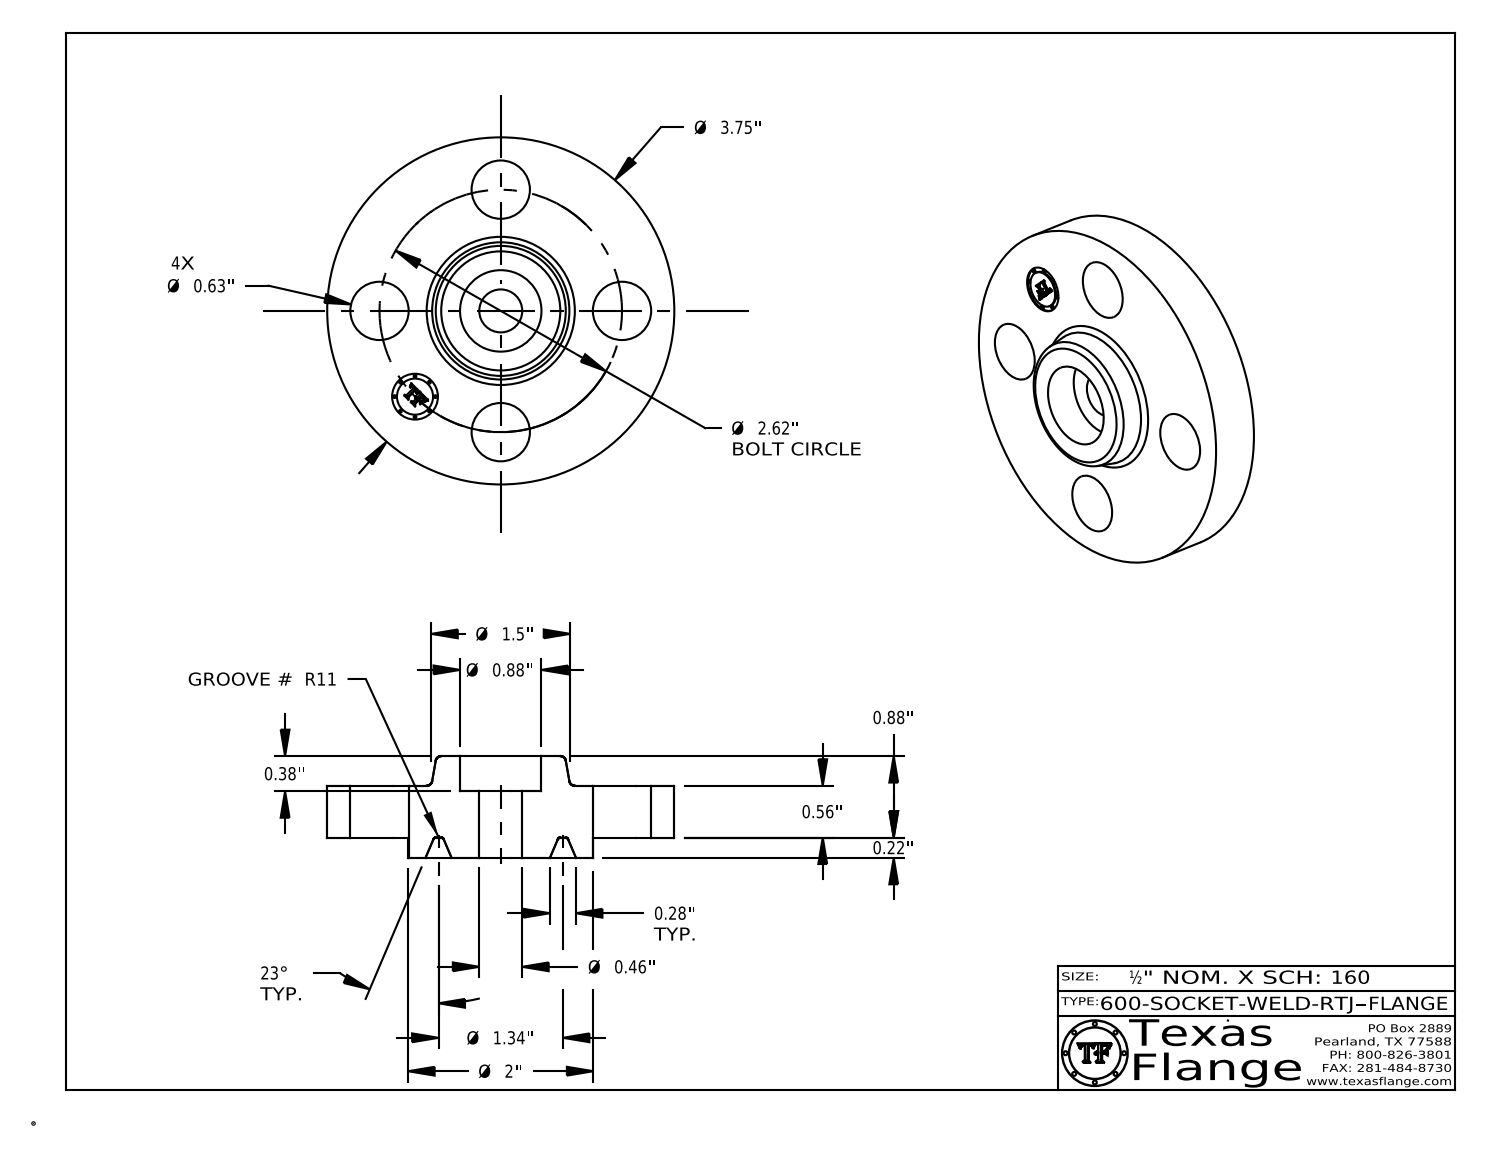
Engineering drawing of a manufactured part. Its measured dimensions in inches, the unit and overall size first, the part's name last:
Units: inches
Overall size (bounding box): 3.75 × 3.75 × 1.099
Round holes (diameter × count): ⌀0.63 ×4, ⌀0.464 ×1, ⌀0.495 ×1, ⌀0.88 ×1
Round bosses / shafts (diameter × count): ⌀0.03 ×8, ⌀3.75 ×1, ⌀2 ×1, ⌀0.39 ×1
Main face-to-face distances: 0.56, 0.219, 0.779, 1.099, 0.88, 0.32, 0.719, 0.5, 0.06, 0.38
Hole centre spacings: 1.31, 1.852, 1.003, 2.42, 2.62, 1.31
Volume: 6.172 in³ · Surface area: 36.1 in²
Bodies: 1 solid, 426 faces (372 planar, 40 cylindrical, 14 other)
Part name (STEP PRODUCT): 600-SOCKET-WELD-RTJ
STEP written by: CATIA V5 STEP AP214 (AUTOMOTIVE_DESIGN)
